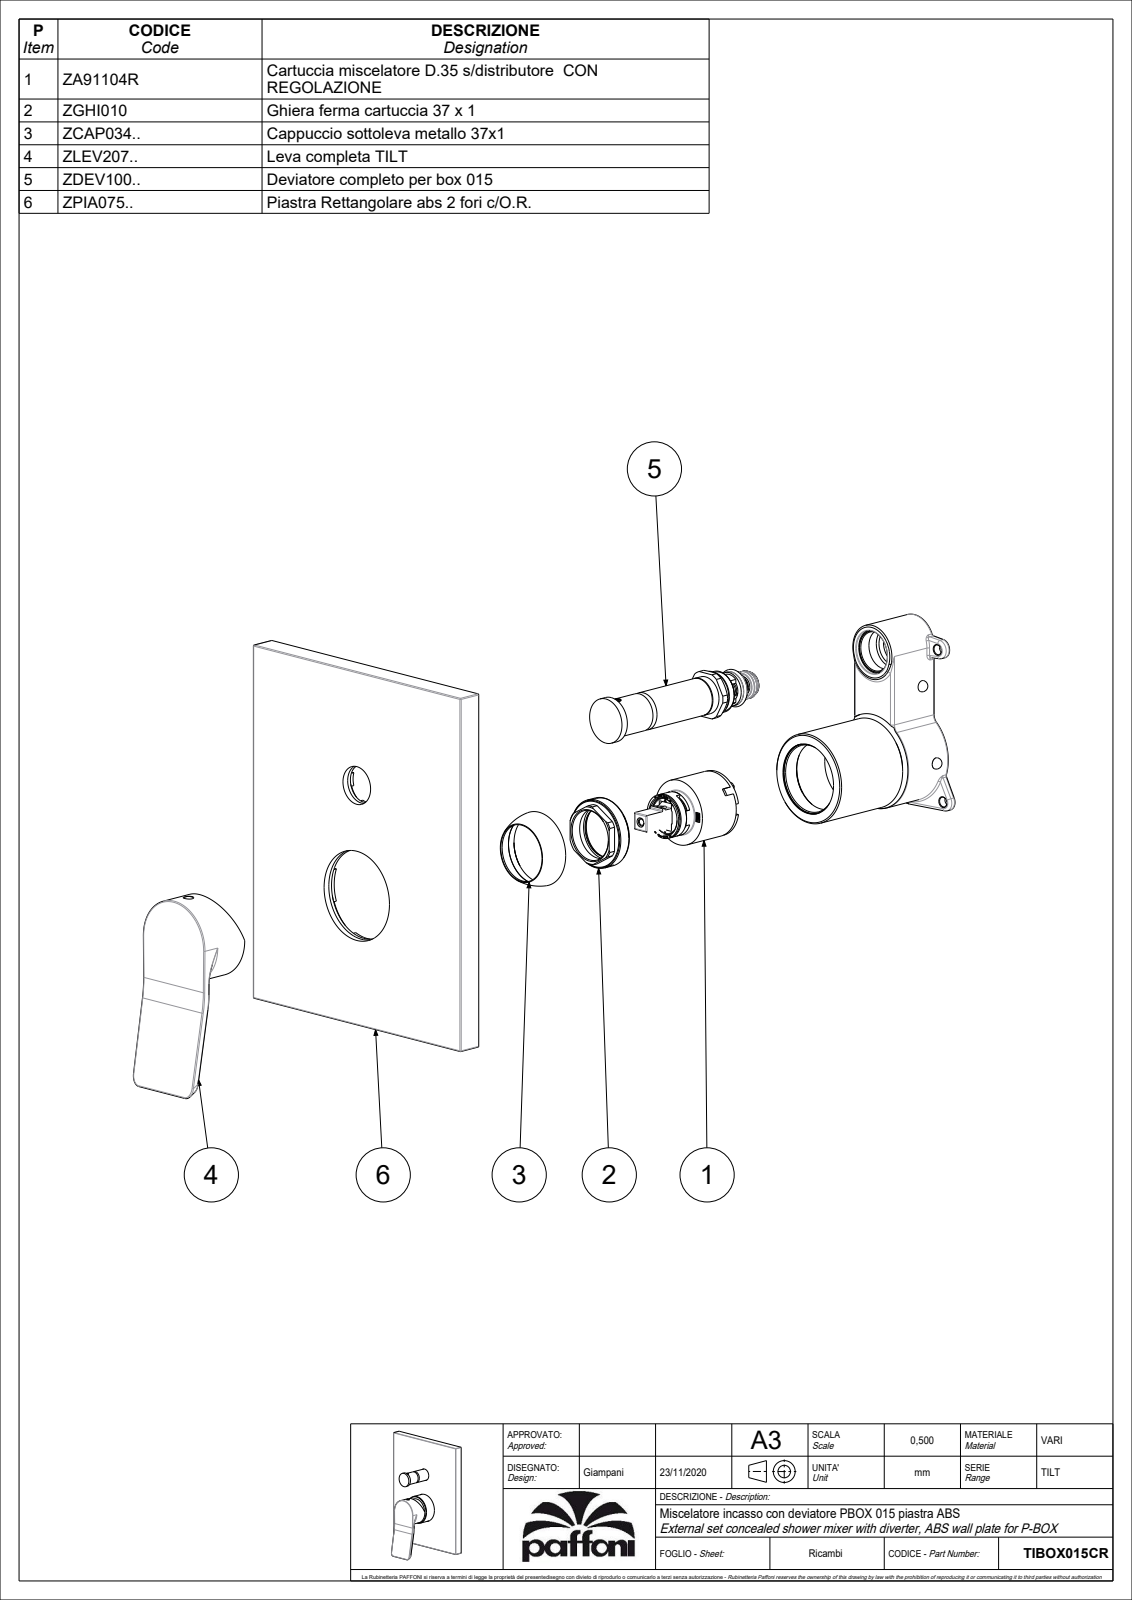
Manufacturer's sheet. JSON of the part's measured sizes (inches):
{"part_name": "TIBOX015CR", "step_written_by": "CREO PARAMETRIC BY PTC INC, 2020044 (CONFIG_CONTROL_DESIGN)", "units": "inches", "bodies": {"solids": 2, "faces": 176, "planar": 53, "cylindrical": 66, "other": 57}, "overall_size": [7.926, 6.063, 2.935], "volume_in3": 27.93, "surface_area_in2": 151.2, "round_holes": [[0.118, 1], [0.165, 1], [0.217, 1], [1.205, 1], [1.417, 1], [1.476, 1]], "round_bosses_or_shafts": [[1.894, 1], [1.791, 1], [0.945, 1], [0.787, 1], [0.591, 1], [0.299, 1]], "partial_cylinders_radius": [[0.02, 18], [0.059, 2], [0.197, 2], [1.738, 1], [2.48, 1]], "face_to_face_distances": [0.531, 6.063, 7.559, 0.158, 2.583, 2.051, 2.425, 1.894, 0.157, 0.787]}
